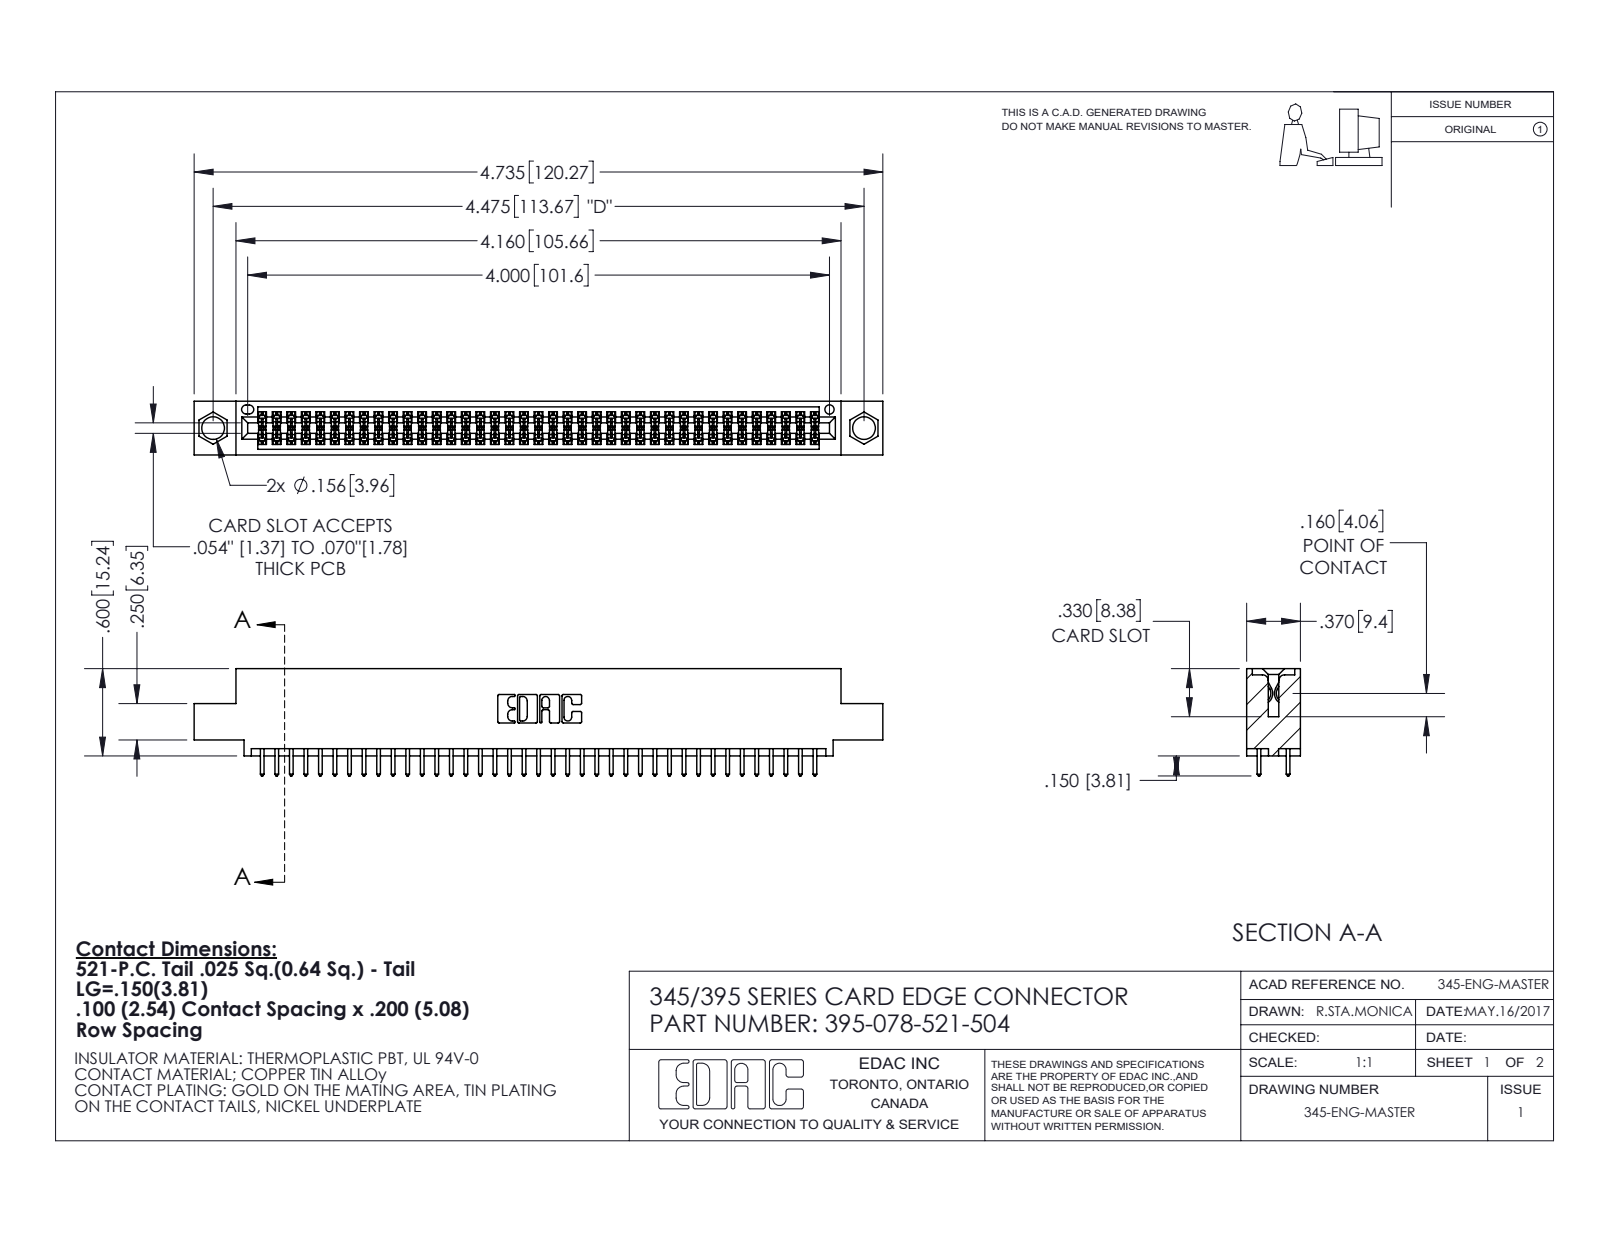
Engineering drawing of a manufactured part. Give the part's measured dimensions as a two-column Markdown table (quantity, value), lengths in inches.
| quantity | value |
| --- | --- |
| part name | 345 Part_0.110 Offset - 0.156 Dia-TI; 395-078-521-504; 345-292-001_345-293-121 |
| STEP written by | SolidWorks 2020 (CONFIG_CONTROL_DESIGN) |
| units | inches |
| bodies | 79 solids, 4044 faces (2672 planar, 1372 cylindrical, 0 other) |
| overall size | 4.735 × 0.737 × 0.37 |
| volume | 0.698 in³ |
| surface area | 25.72 in² |
| round holes (diameter × count) | 0.156 × 2, 0.064 × 1 |
| partial cylindrical surfaces (radius × count) | 0.006 × 156, 0.01 × 78, 0.01 × 22, 0.007 × 6, 0.031 × 6, 0.026 × 3, 0.014 × 2, 0.019 × 2 |
| main face-to-face distances | 0.072, 0.298, 0.2, 0.37, 0.098, 0.272, 0.025, 0.225, 0.175, 0.149 |
| hole center spacings | 0.27, 4.239, 4.475 |
